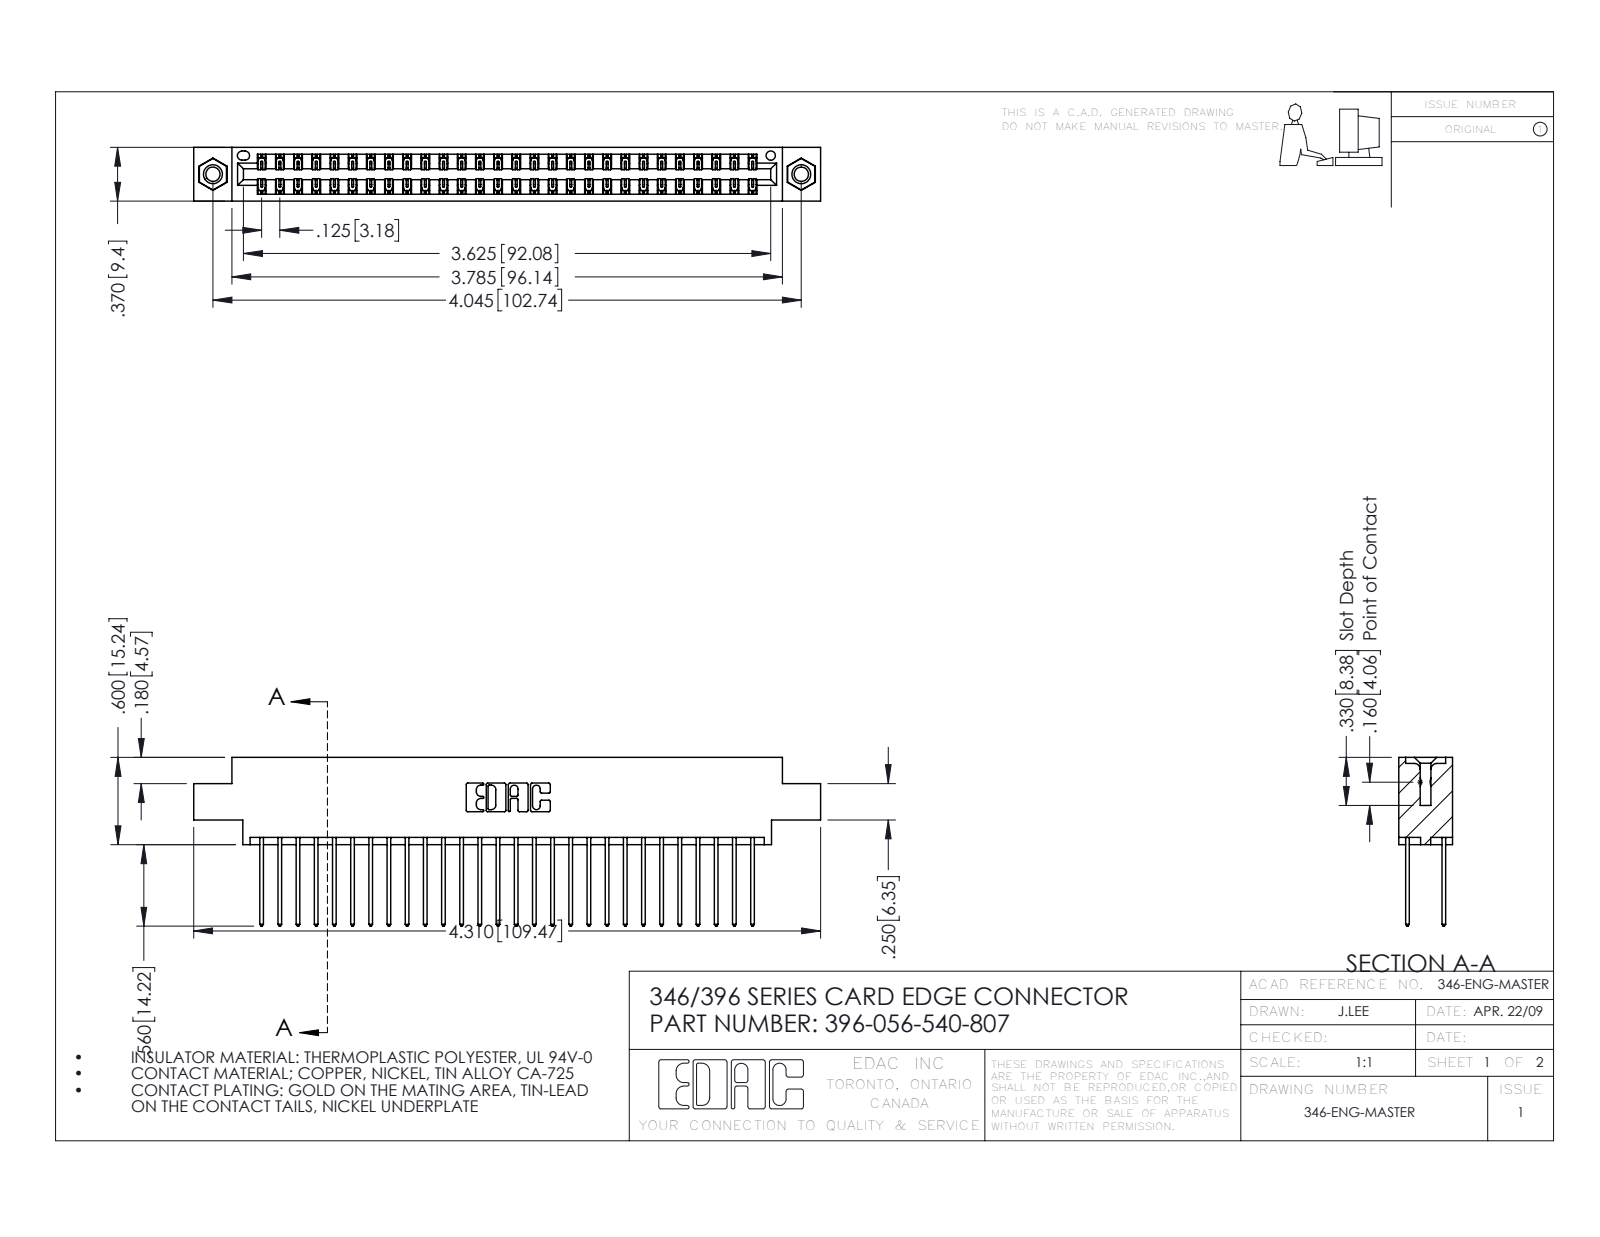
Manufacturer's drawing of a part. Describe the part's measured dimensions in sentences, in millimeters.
The part is named "345-292-001_345-293-140; 346 Part_0.170 Offset - 0.156 Dia-TI; 345-250-001_345-250-005-103; 396-056-540-807". Its 3-D file was written by "SolidWorks 2016 (CONFIG_CONTROL_DESIGN)". It is 59 solids with 3098 faces: 2072 planar, 1010 cylindrical and 16 other. Overall it measures 109.5 by 29.5 by 9.4 millimeters. Its volume is 10 600 cubic millimeters and its surface area 15 580 square millimeters. Round holes: 2 of diameter 2.5, 2 of diameter 3.2, 2 of diameter 4, 1 of diameter 1.6. Round bosses or shafts: 2 of diameter 3.9. Partial cylindrical surfaces (rounded edges, fillets, slot ends): 84 of radius 0.2, 56 of radius 0.3, 22 of radius 0.3, 6 of radius 0.2, 6 of radius 0.8, 3 of radius 0.7, 2 of radius 0.4, 2 of radius 0.6. The main face-to-face distances are 1.2, 8.2, 6.4, 9.4, 1.8, 7.6, 0.6, 7, 5.6, 3.8. The hole center spacings are 6.2, 97.5, 102.7.
